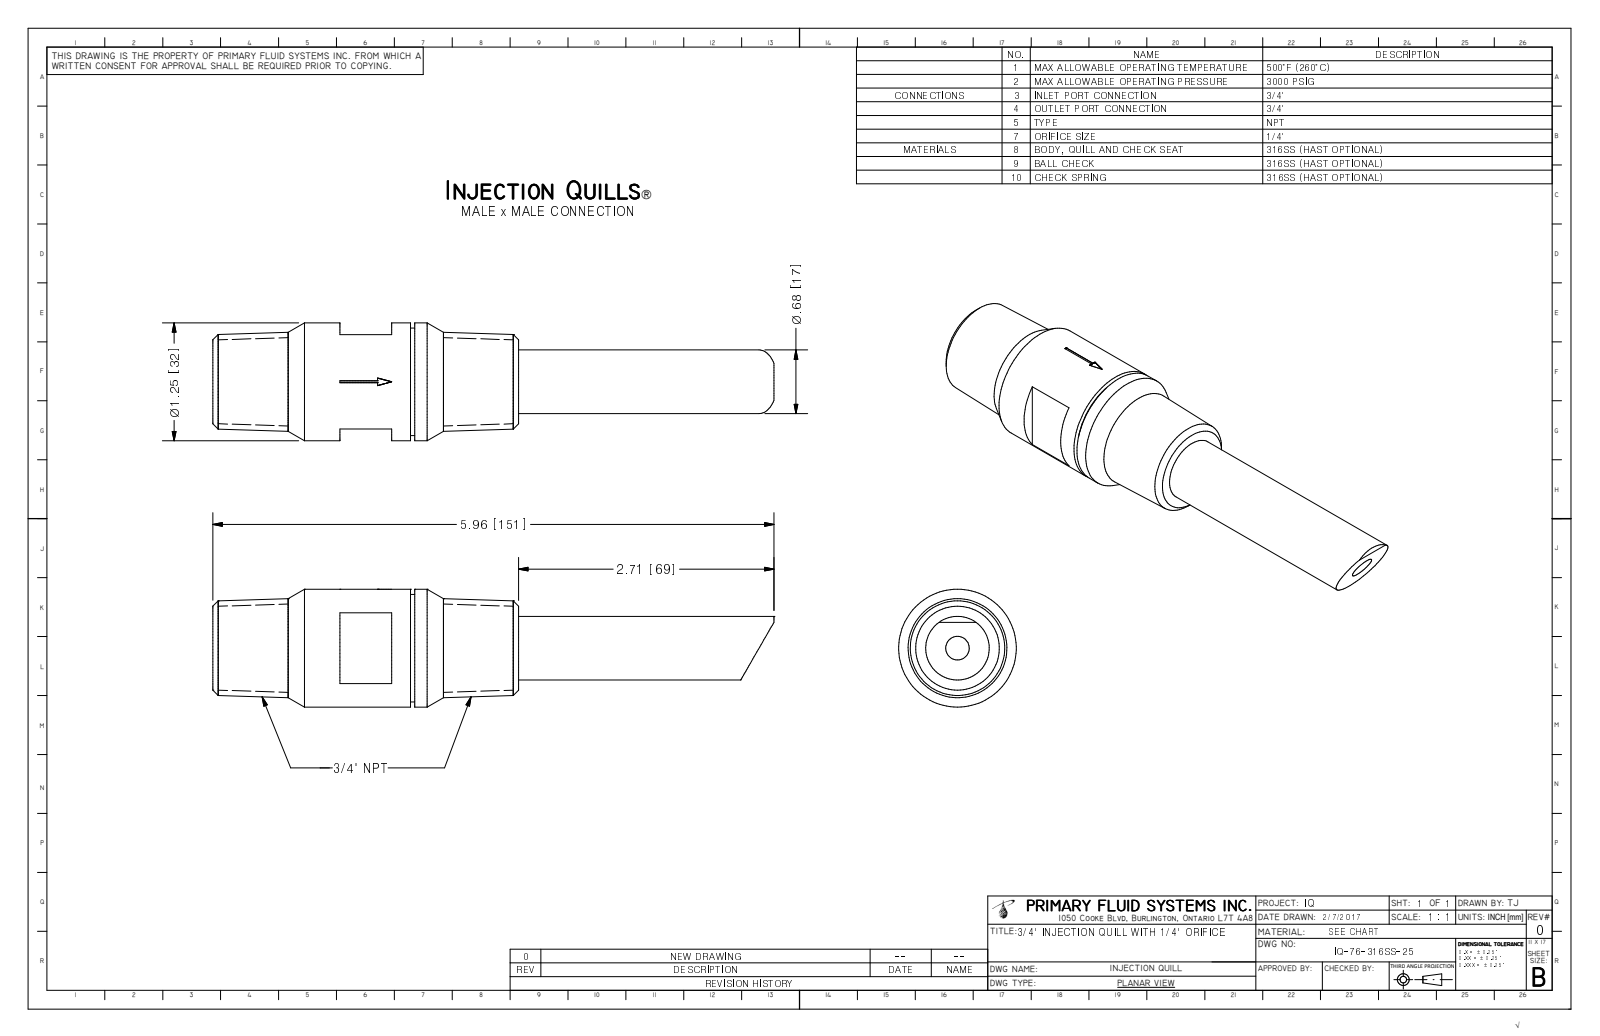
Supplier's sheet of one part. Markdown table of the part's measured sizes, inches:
| quantity | value |
| --- | --- |
| part name | IQ-76-316SS-25_R0 |
| STEP written by | Autodesk Inventor 2009 (AUTOMOTIVE_DESIGN) |
| units | inches |
| bodies | 1 solid, 34 faces (19 planar, 7 cylindrical, 8 other) |
| overall size | 5.964 × 1.25 × 1.25 |
| volume | 3.802 in³ |
| surface area | 23.03 in² |
| round holes (diameter × count) | 0.25 × 1, 0.469 × 1 |
| round bosses / shafts (diameter × count) | 1.25 × 1, 1.14 × 1, 0.675 × 1 |
| partial cylindrical surfaces (radius × count) | 0.624 × 1 |
| main face-to-face distances | 1, 1.35, 1.15, 0.75, 3.25, 1.9, 2.1, 2.145, 0.045, 1.105 |
